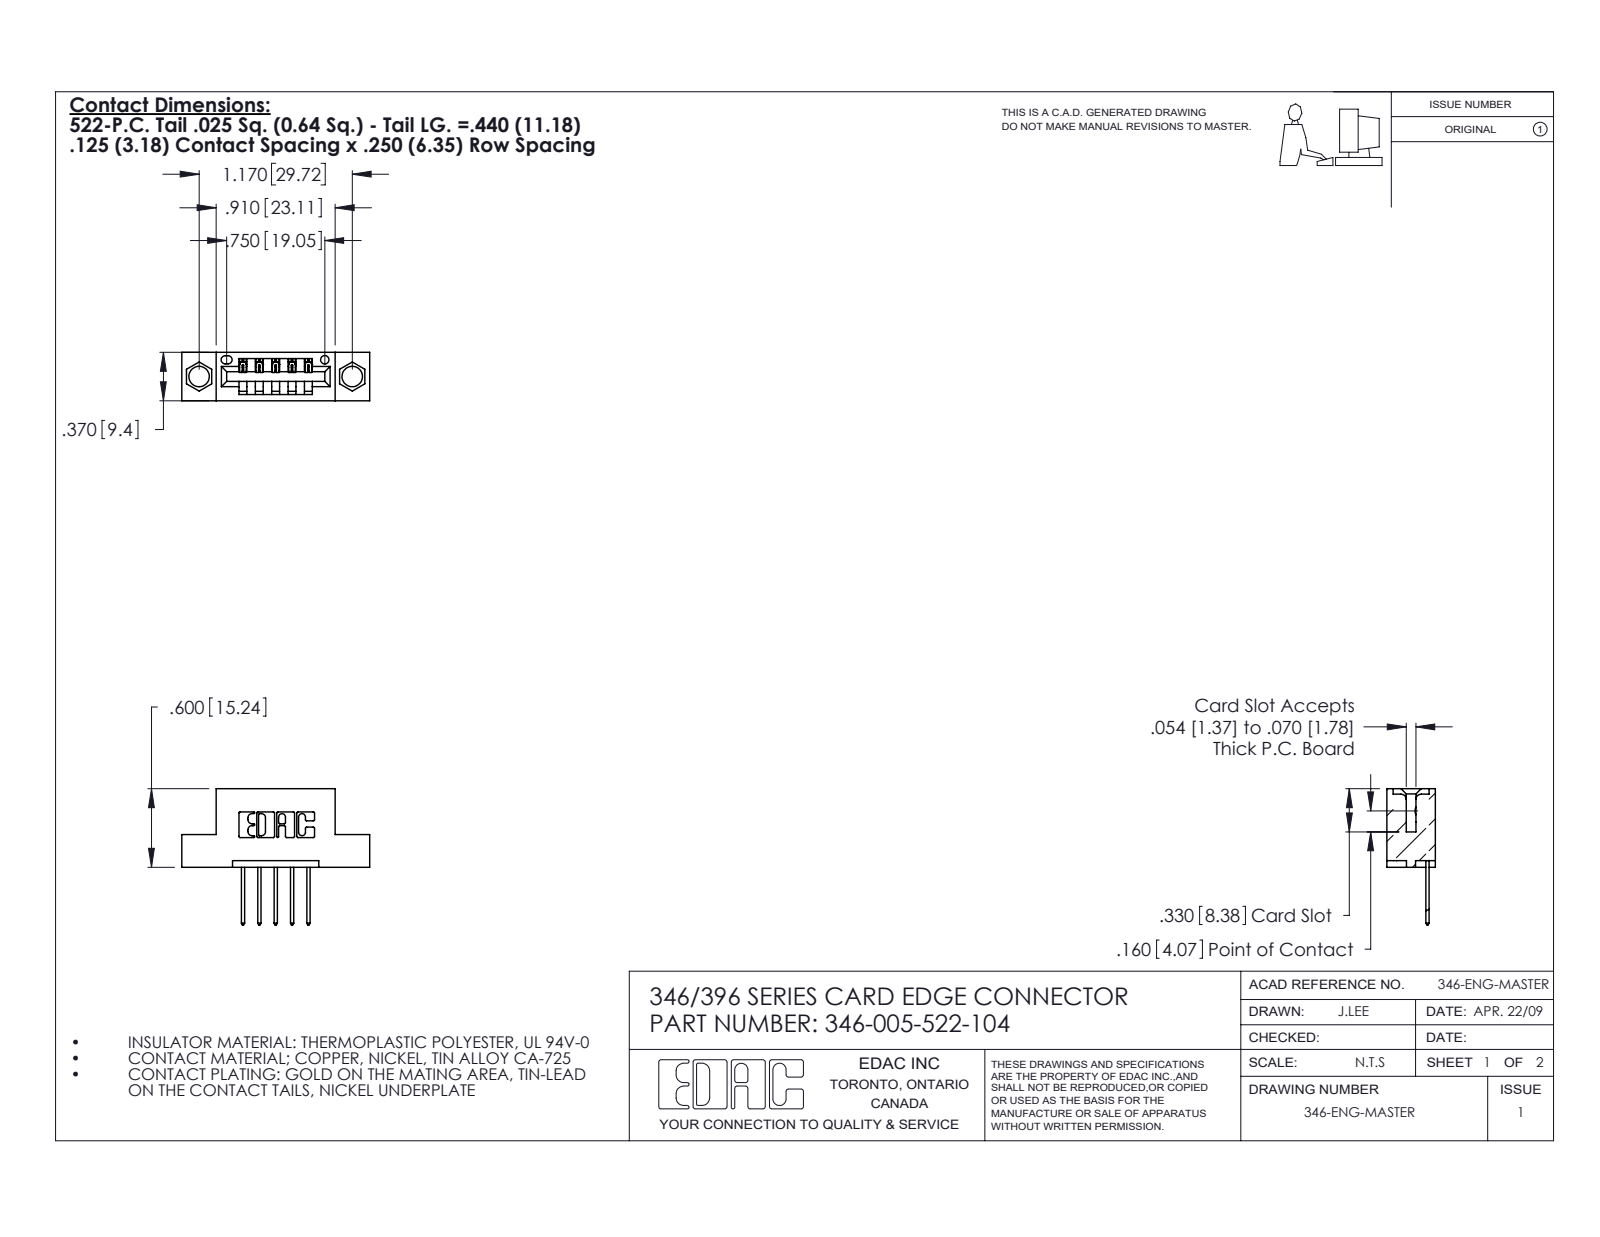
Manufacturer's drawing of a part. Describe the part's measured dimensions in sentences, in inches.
The part is named "346-005-522-104; 346 Part_Flush Mounting Lugs - 0.156 Dia-TH; 345-292-001_345-293-122". Its 3-D file was written by "SolidWorks 2020 (CONFIG_CONTROL_DESIGN)". It is 6 solids with 426 faces: 290 planar, 136 cylindrical and 0 other. Overall it measures 1.435 by 1.04 by 0.37 inches. Its volume is 0.191 cubic inches and its surface area 5.219 square inches. Round holes: 2 of diameter 0.156, 1 of diameter 0.064. Partial cylindrical surfaces (rounded edges, fillets, slot ends): 22 of radius 0.01, 10 of radius 0.006, 10 of radius 0.01, 6 of radius 0.007, 6 of radius 0.031, 3 of radius 0.026, 2 of radius 0.031, 2 of radius 0.04. The main face-to-face distances are 0.25, 0.37, 0.048, 0.322, 0.148, 0.222, 0.1, 0.174, 0.55, 0.072. The hole center spacings are 0.246, 0.969, 1.17.
